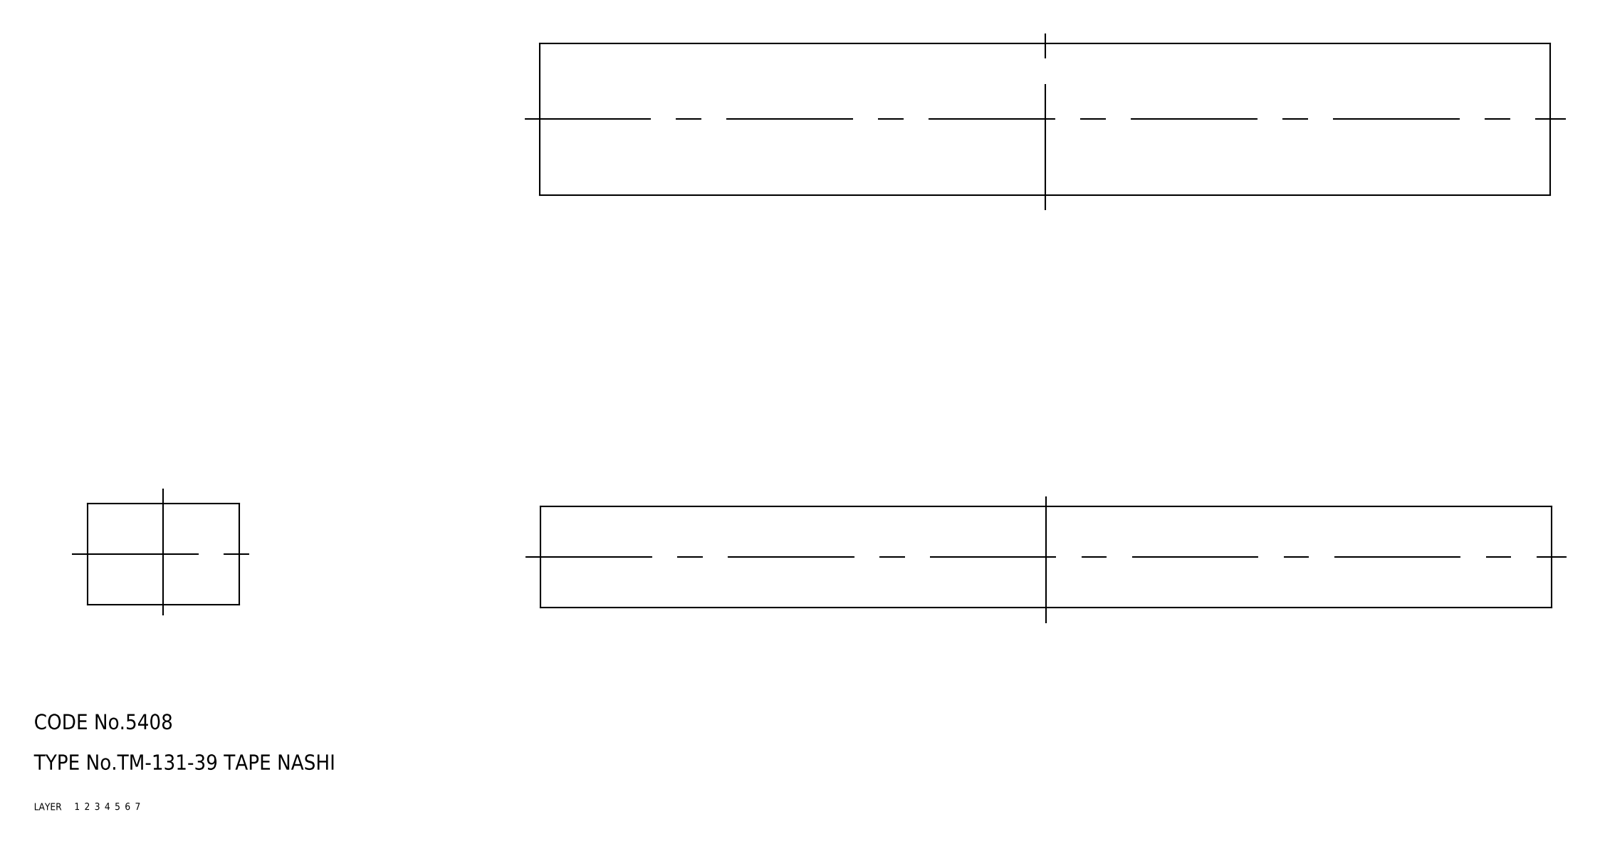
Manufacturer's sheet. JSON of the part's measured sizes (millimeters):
{"part_name": "rubber foam", "step_written_by": "CADfix (AUTOMOTIVE_DESIGN)", "units": "millimeters", "bodies": {"solids": 1, "faces": 6, "planar": 0, "cylindrical": 0, "other": 6}, "overall_size": [200, 30, 20], "volume_mm3": 120000, "surface_area_mm2": 21200}
